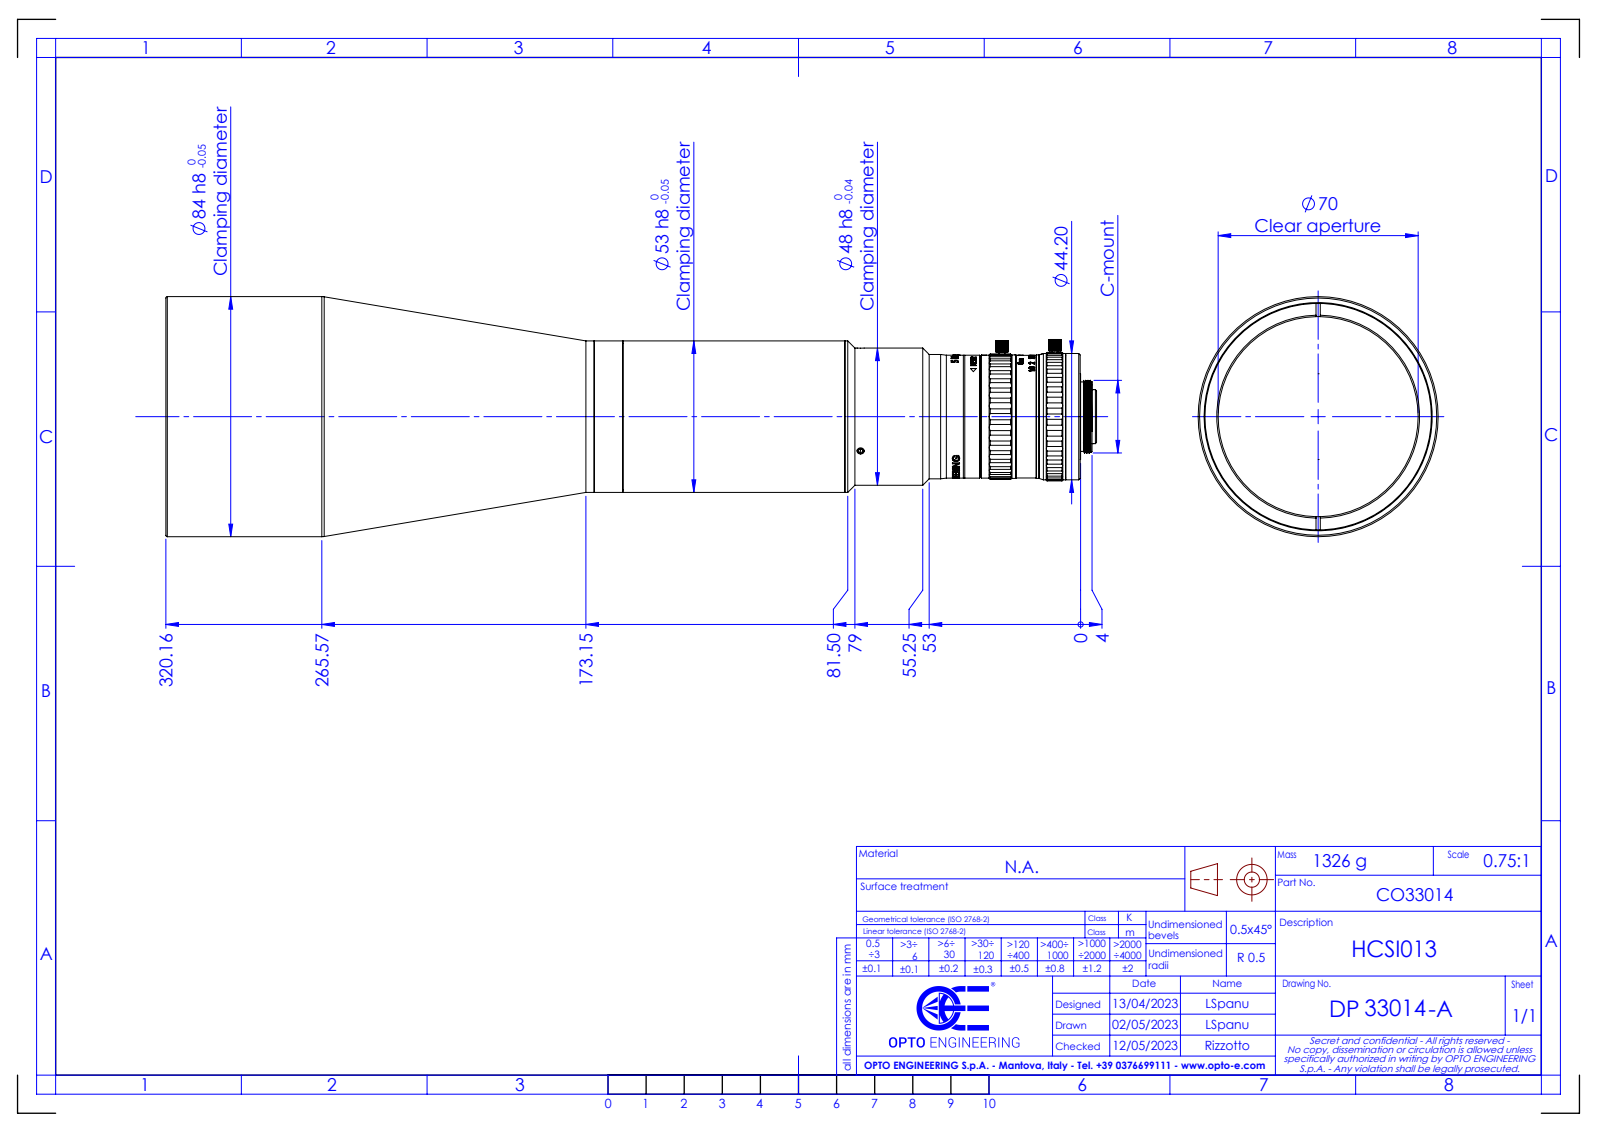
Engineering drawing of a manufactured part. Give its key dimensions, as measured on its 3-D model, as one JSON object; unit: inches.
{"part_name": "DP33014-A_HCSI013", "step_written_by": "SolidWorks 2021 (CONFIG_CONTROL_DESIGN)", "units": "inches", "bodies": {"solids": 0, "faces": 559, "planar": 106, "cylindrical": 364, "other": 89}, "overall_size": [12.824, 3.307, 3.307], "round_holes": [[0.098, 3], [0.102, 1], [0.535, 1], [0.846, 1], [1.633, 1], [2.756, 1], [3.12, 1]], "round_bosses_or_shafts": [[3.307, 1], [2.087, 1], [1.89, 1], [1.74, 1], [1.713, 1], [1.701, 1], [1.693, 1], [1.691, 1]], "partial_cylinders_radius": [[0.079, 72], [0.089, 2], [0.039, 1], [0.84, 1], [0.843, 1], [0.864, 1], [0.886, 1]], "face_to_face_distances": [0.108, 9.337, 9.228, 12.579, 12.47, 3.242, 6.299, 6.28, 6.171, 3.057], "hole_center_spacings": [0.689]}
